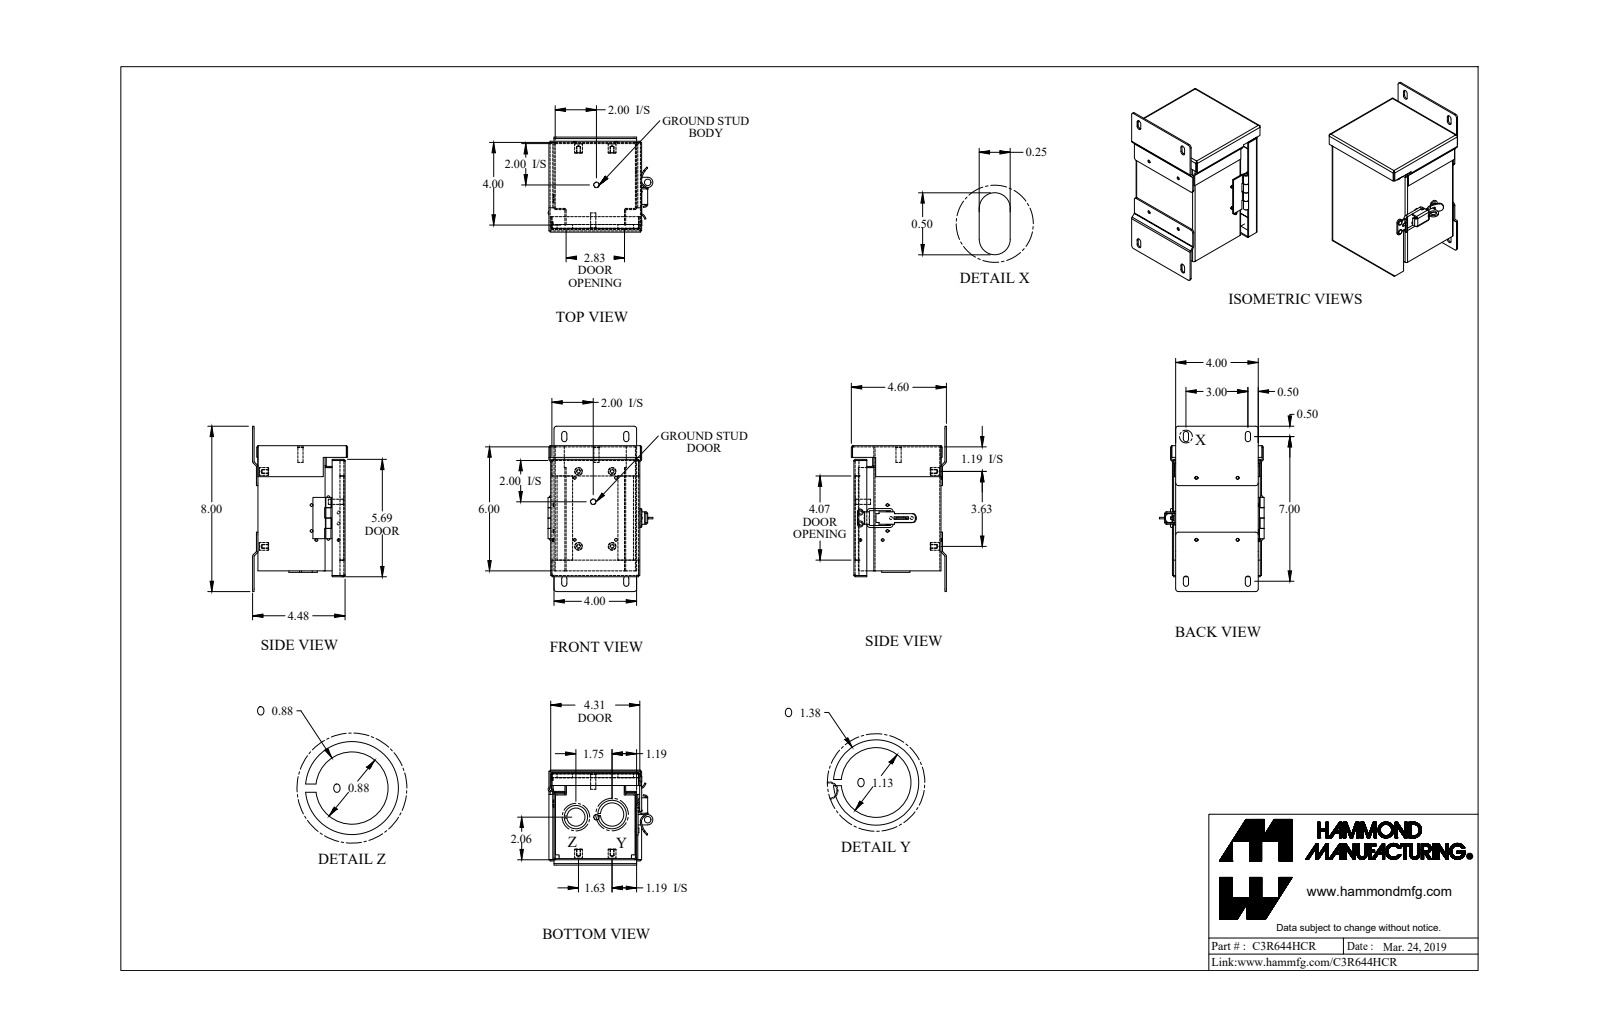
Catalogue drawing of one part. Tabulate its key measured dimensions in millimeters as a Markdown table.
| quantity | value |
| --- | --- |
| part name | C3R644HCR_Default |
| STEP written by | SolidWorks 2019 (CONFIG_CONTROL_DESIGN) |
| units | millimeters |
| bodies | 28 solids, 721 faces (418 planar, 250 cylindrical, 53 other) |
| overall size | 203.2 × 128.8 × 116.8 |
| volume | 240 700 mm³ |
| surface area | 296 800 mm² |
| round holes (diameter × count) | 3.5 × 4, 3.6 × 4, 4 × 4, 3.4 × 2, 3.7 × 2, 3.2 × 1, 3.3 × 1, 8 × 1, 22.2 × 1, 28.6 × 1 |
| round bosses / shafts (diameter × count) | 3.3 × 8, 9.5 × 4, 3.2 × 4, 2.5 × 4, 7.1 × 2, 6.4 × 2, 34.9 × 1, 28.6 × 1 |
| partial cylindrical surfaces (radius × count) | 0.7 × 28, 2.2 × 28, 3.2 × 21, 0.9 × 6, 2.7 × 6, 3.4 × 2, 1 × 1, 1.7 × 1 |
| main face-to-face distances | 1.4, 105.7, 4.7, 100.2, 6.2, 101.6, 104.2, 152.4, 107.1, 98.7 |
| hole center spacings | 41.3, 46.7, 46.7, 50.8, 63.4, 76.2, 91.6, 92.1 |
